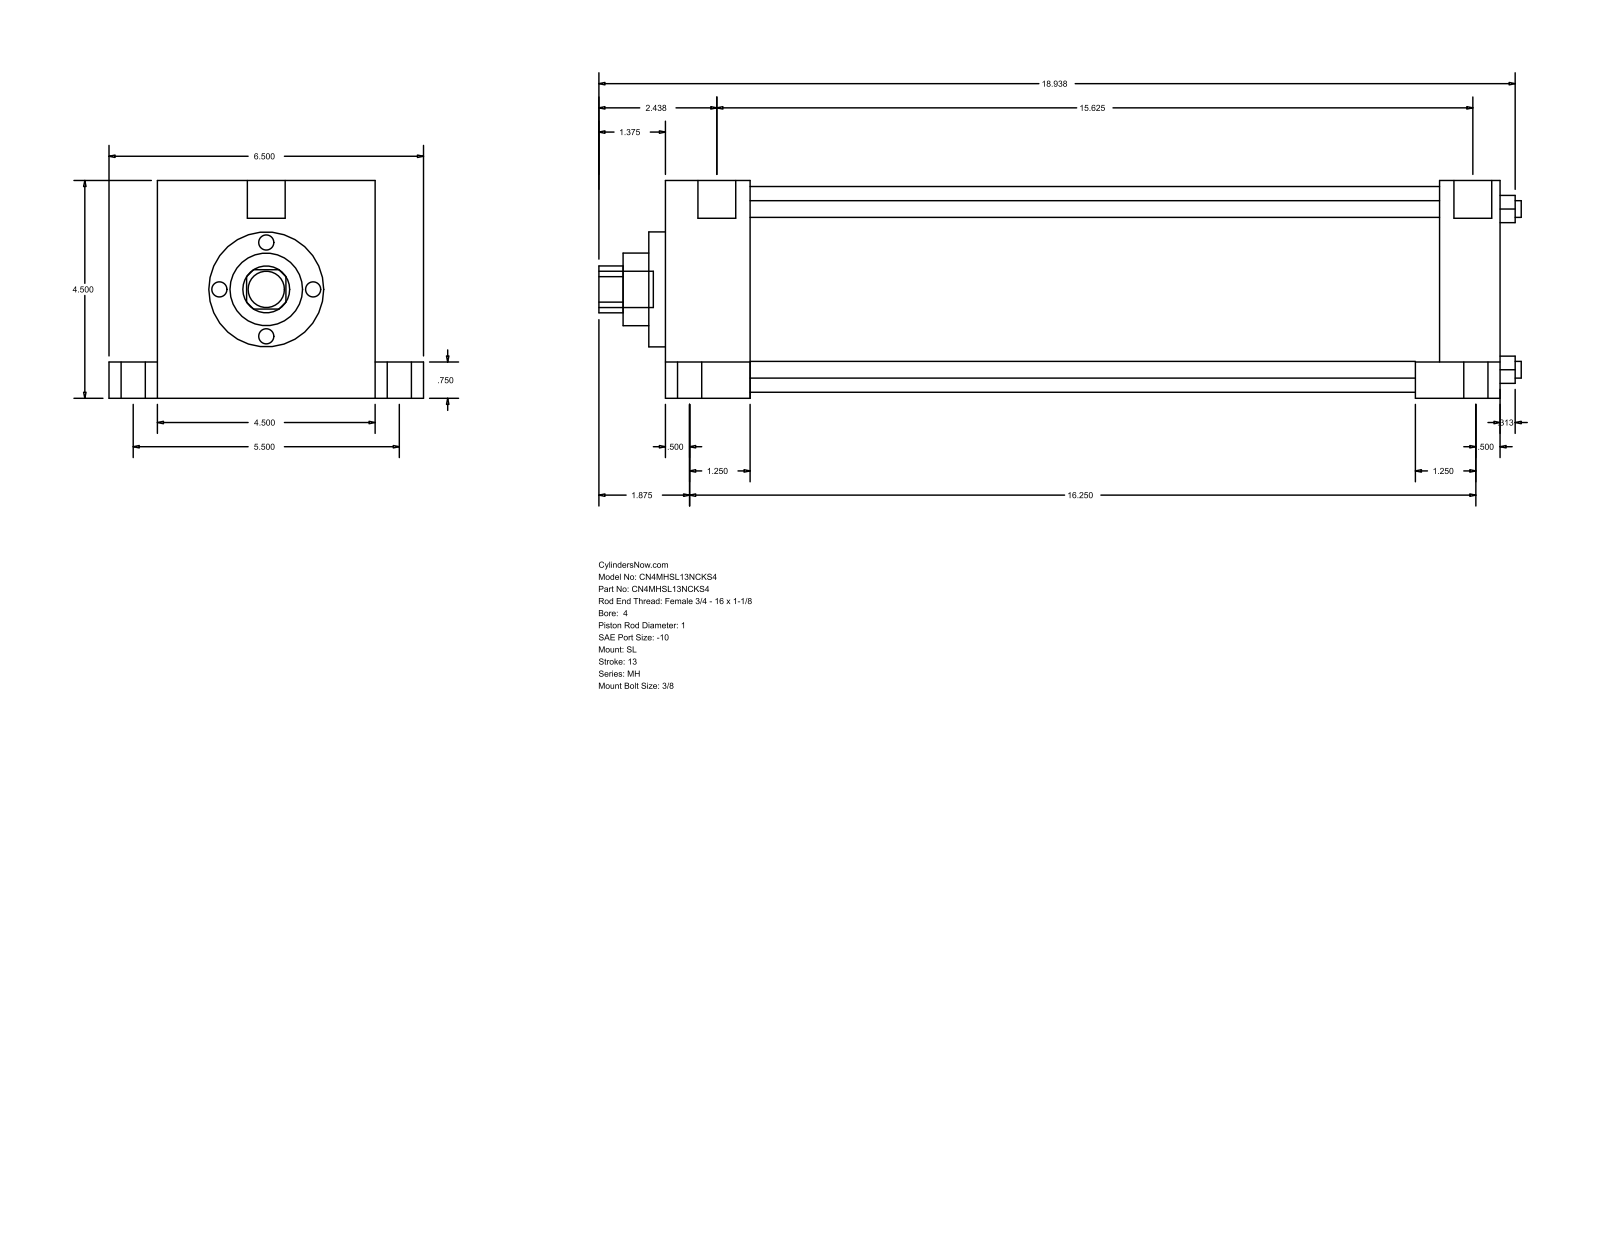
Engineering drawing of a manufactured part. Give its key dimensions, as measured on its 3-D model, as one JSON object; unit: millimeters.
{"part_name": "MH_SL__0400_1", "step_written_by": "GSSL Pune (CONFIG_CONTROL_DESIGN)", "units": "millimeters", "bodies": {"solids": 0, "faces": 110, "planar": 77, "cylindrical": 33, "other": 0}, "overall_size": [484.19, 165.1, 114.3], "round_holes": [[8.76, 4], [25.4, 1], [38.1, 1], [60.33, 1], [107.95, 1]], "round_bosses_or_shafts": [[19.05, 5], [12.7, 4], [8.73, 4], [19.84, 2]], "partial_cylinders_radius": [[12.29, 1]], "face_to_face_distances": [114.3, 438.15, 44.46, 393.69, 406.4, 361.94, 31.75, 25.4, 139.7, 19.05], "hole_center_spacings": [59.62, 84.32, 119.25]}
